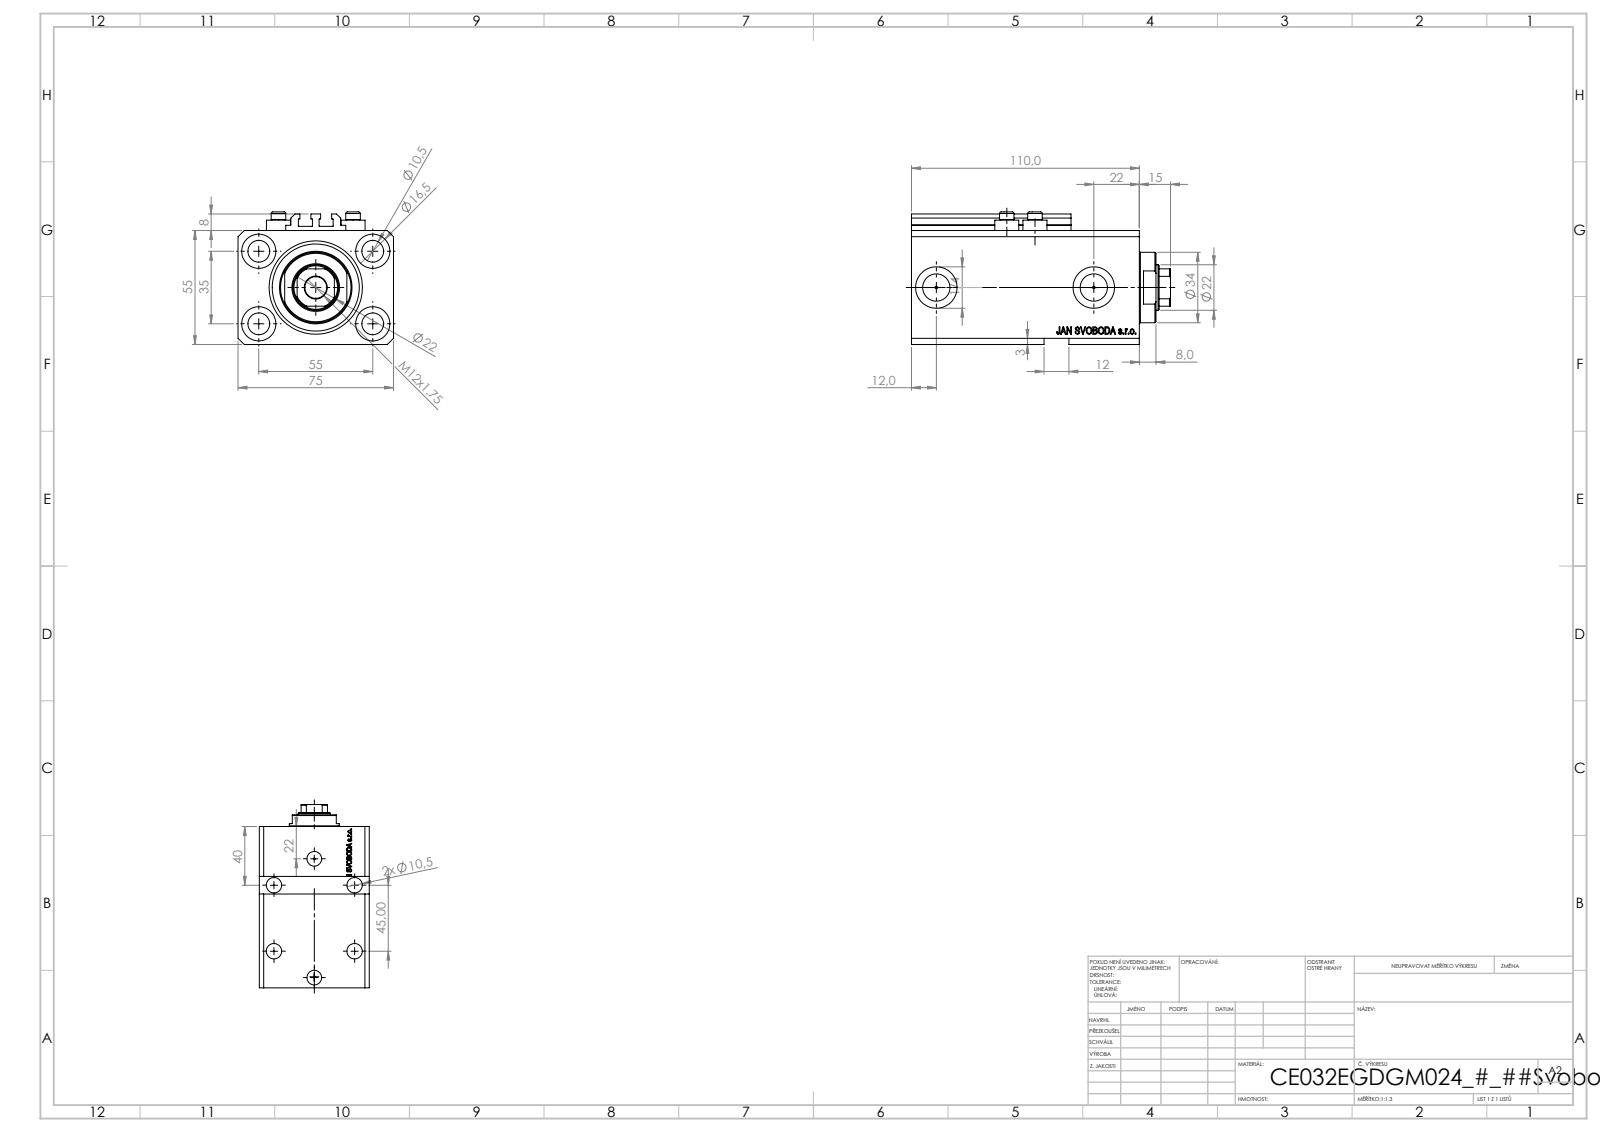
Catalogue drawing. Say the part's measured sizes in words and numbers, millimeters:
The part is named "V250CE_E_Body; ALLEN BOLT V250CE; V250CE_VC_E; V250CE_C_VCP". Its 3-D file was written by "SolidWorks 2019 (CONFIG_CONTROL_DESIGN)". It is 8 solids with 1100 faces: 518 planar, 158 cylindrical and 424 other. Overall it measures 125 by 75 by 64 millimeters. Its volume is 377 718 cubic millimeters and its surface area 96 791 square millimeters. Round holes: 9 of diameter 10.5, 4 of diameter 1.25, 4 of diameter 4, 4 of diameter 16.5, 2 of diameter 10, 2 of diameter 13.16, 2 of diameter 20, 1 of diameter 22, 1 of diameter 32, 1 of diameter 45. Round bosses or shafts: 4 of diameter 11.6, 4 of diameter 7, 1 of diameter 34. Partial cylindrical surfaces (rounded edges, fillets, slot ends): 10 of radius 0.2, 1 of radius 10.5. The main face-to-face distances are 55, 75, 15, 110, 95, 9.9, 3, 85.1, 100.1, 57. The hole center spacings are 32.6, 32.87, 55, 68.74, 13.6, 14.09, 23.05, 25.81.
